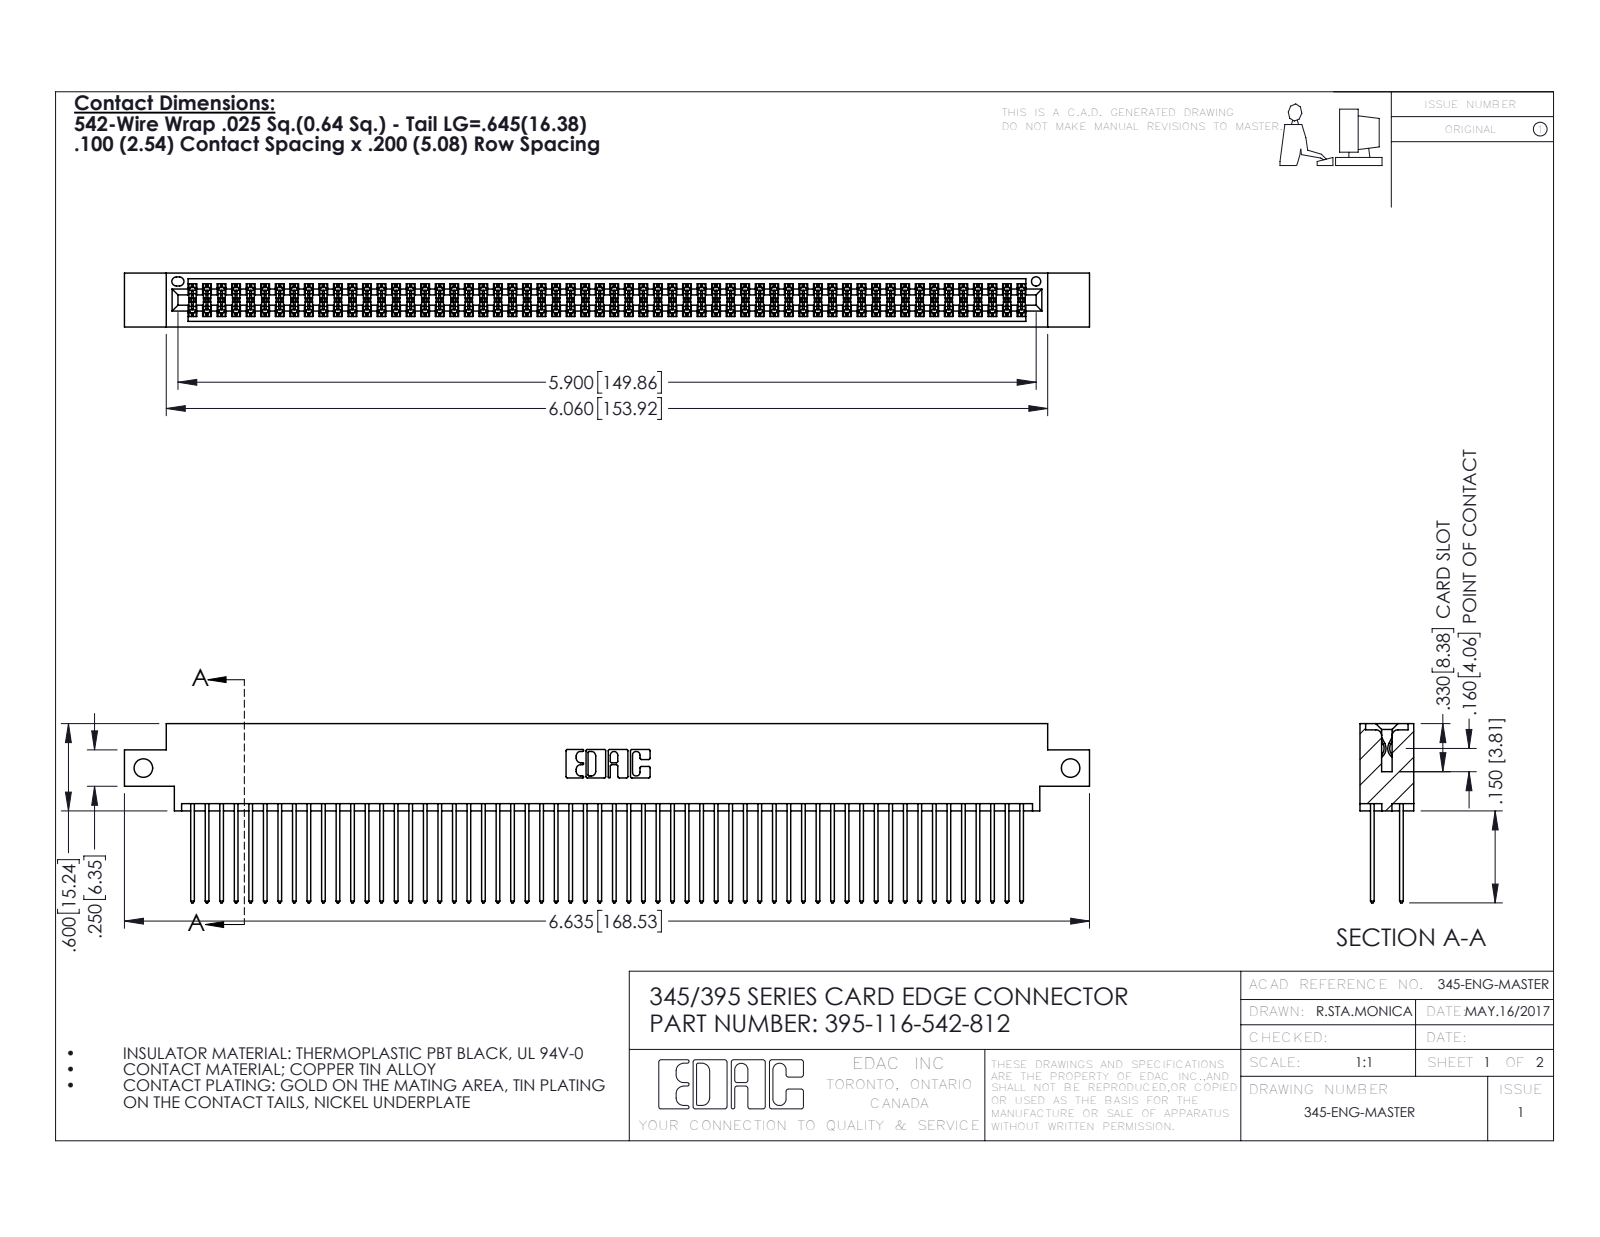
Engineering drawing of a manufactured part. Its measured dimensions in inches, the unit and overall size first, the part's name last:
Units: inches
Overall size (bounding box): 6.635 × 1.232 × 0.37
Round holes (diameter × count): ⌀0.128 ×2, ⌀0.064 ×1
Partial cylindrical surfaces — rounded edges, fillets, slot ends (radius × count): R0.006 ×174, R0.01 ×116, R0.01 ×22, R0.007 ×6, R0.031 ×6, R0.026 ×3, R0.014 ×2, R0.019 ×2
Main face-to-face distances: 0.298, 0.072, 0.2, 0.098, 0.272, 0.025, 0.37, 0.225, 0.175, 0.149
Hole centre spacings: 6.375
Volume: 1.029 in³ · Surface area: 43.04 in²
Bodies: 117 solids, 5930 faces (3912 planar, 2018 cylindrical, 0 other)
Part name (STEP PRODUCT): 345 Part_0.170 Offset - Side Mount; 345-292-001_345-293-142; 395-116-542-812
STEP written by: SolidWorks 2016 (CONFIG_CONTROL_DESIGN)
